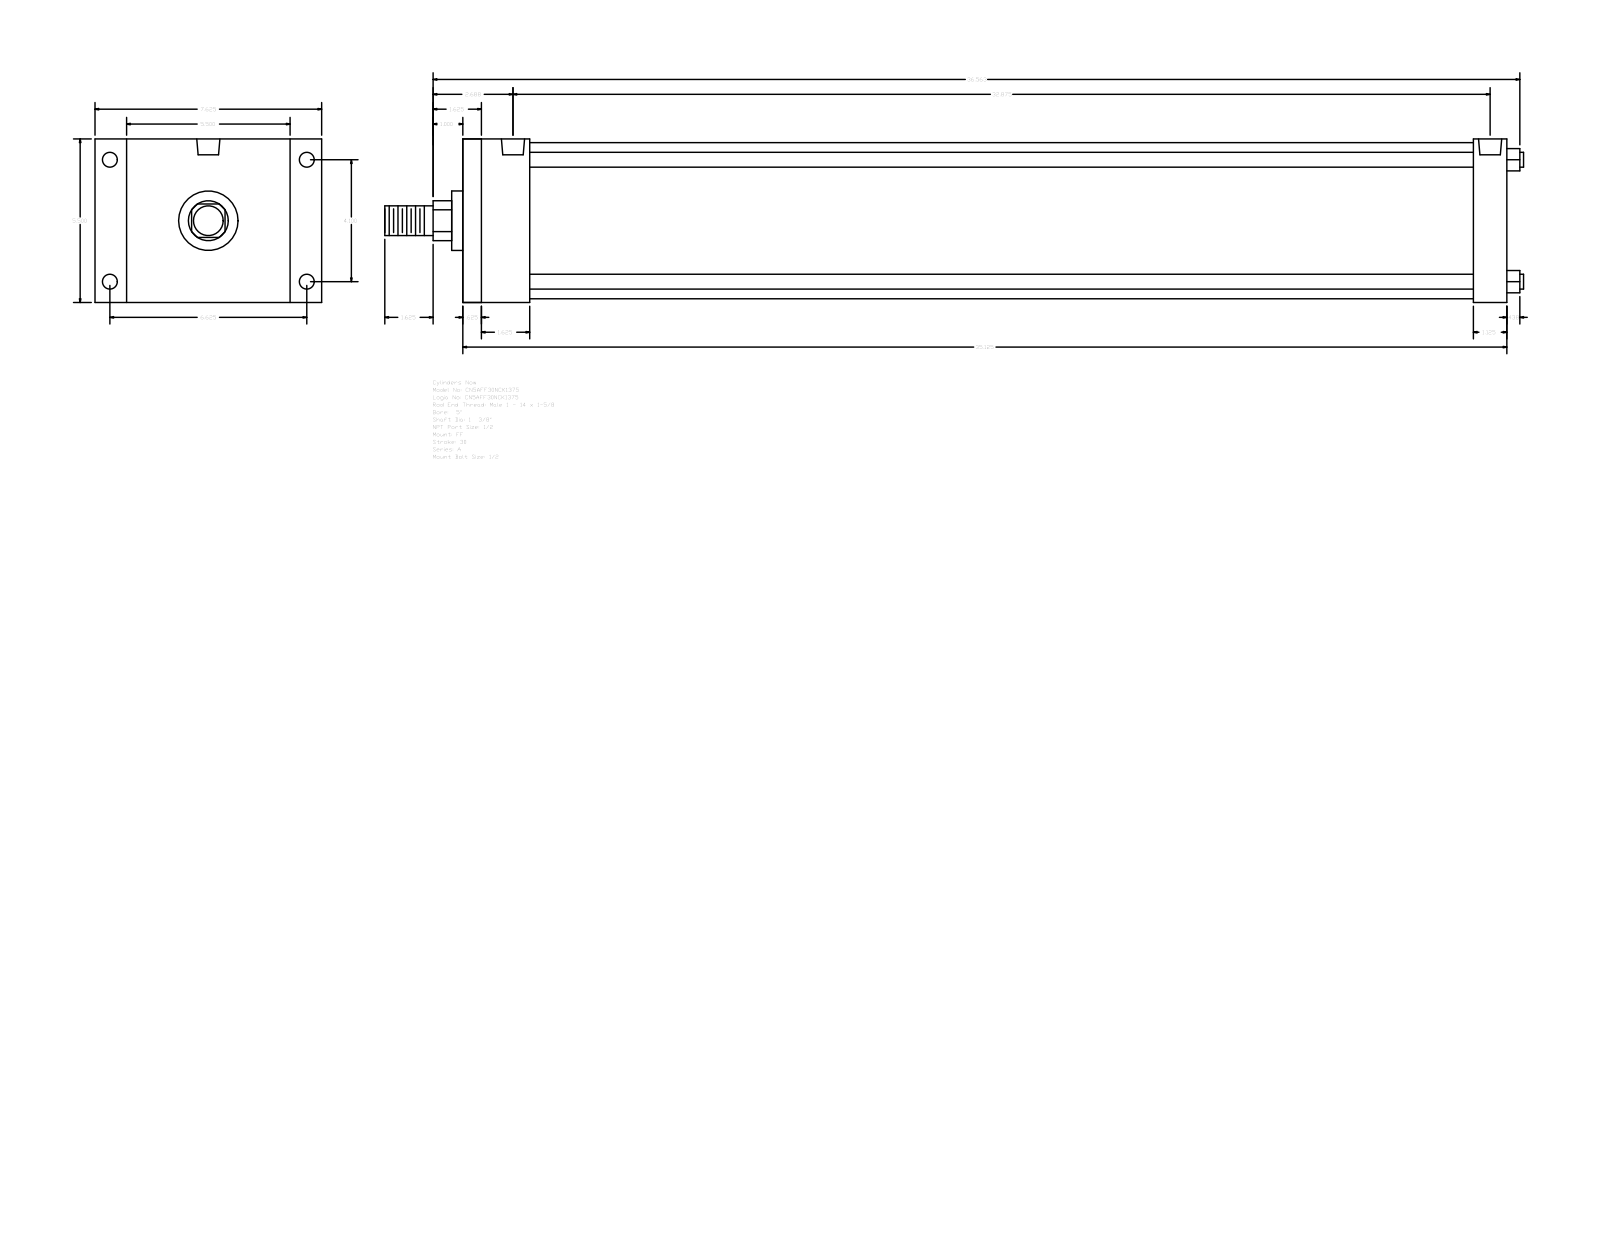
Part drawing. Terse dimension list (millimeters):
name: A_FF__0500_1.375
written by: GSSL Pune (CONFIG_CONTROL_DESIGN)
unit: mm
bodies: 0 solids, 92 faces (64 planar, 28 cylindrical, 0 other)
size: 973.14 × 193.68 × 139.7
holes: 4× ⌀8.73, 4× ⌀12.7, 2× ⌀19.77
bosses: 4× ⌀12.7, 1× ⌀133.35, 1× ⌀50.8, 1× ⌀34.92, 1× ⌀25.4
rounds: 1× R17.06
face distances: 139.7, 892.18, 15.87, 876.31, 57.15, 28.58, 863.6, 847.73, 41.28, 806.45
hole spacings: 2.39, 104.14, 168.28, 197.9, 830.25, 832.64, 835.03
